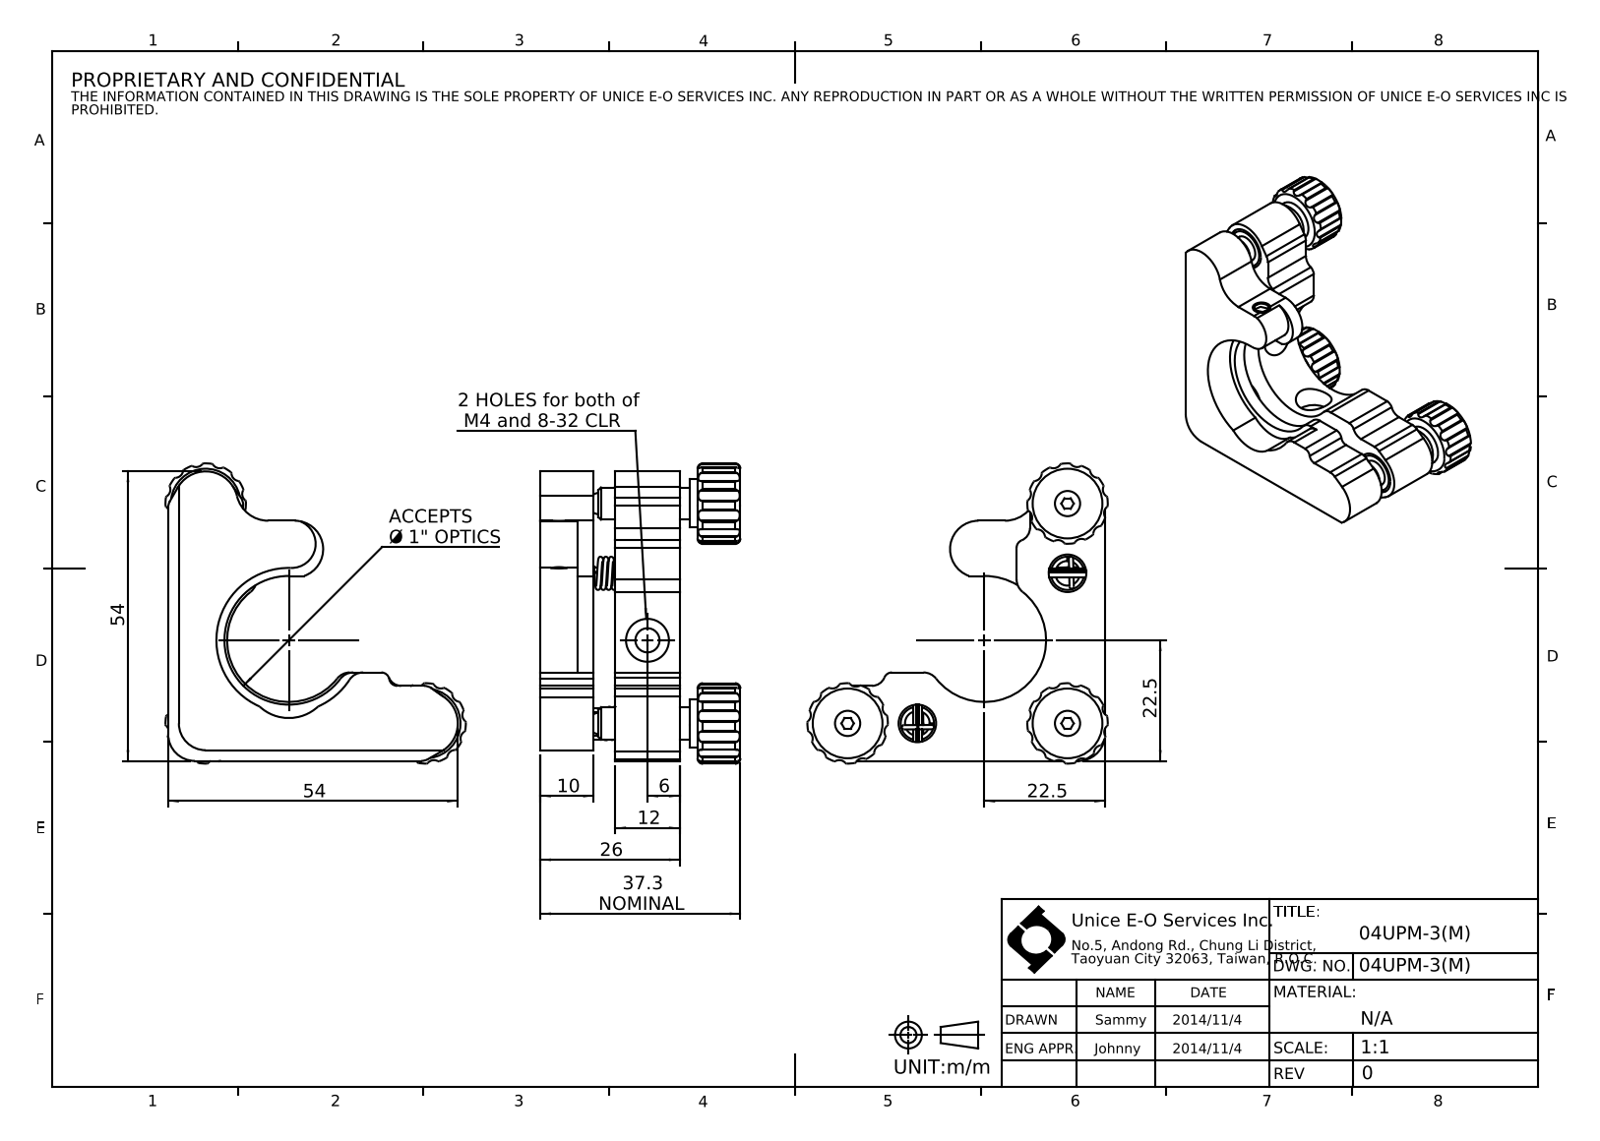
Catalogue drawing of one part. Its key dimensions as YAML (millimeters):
part_name: "04UPM-3(M)"
step_written_by: "SolidWorks 2016 (CONFIG_CONTROL_DESIGN)"
units: millimeters
bodies: {solids: 24, faces: 484, planar: 119, cylindrical: 294, other: 71}
overall_size: [55.95, 55.95, 37.33]
volume: 28064
surface_area: 19263
round_holes:
  - {diameter: 1.2, count: 4}
  - {diameter: 1.7, count: 4}
  - {diameter: 4, count: 3}
  - {diameter: 4.7, count: 3}
  - {diameter: 5.9, count: 3}
  - {diameter: 6, count: 3}
  - {diameter: 9.5, count: 3}
  - {diameter: 4.5, count: 2}
  - {diameter: 7, count: 2}
  - {diameter: 8, count: 2}
  - {diameter: 3.3, count: 1}
  - {diameter: 6.35, count: 1}
round_bosses_or_shafts:
  - {diameter: 1.6, count: 4}
  - {diameter: 9, count: 3}
  - {diameter: 0.6, count: 2}
  - {diameter: 6.3, count: 1}
  - {diameter: 4, count: 1}
  - {diameter: 2.5, count: 1}
partial_cylinders:
  - {radius: 0.3, count: 72}
  - {radius: 1.5, count: 39}
  - {radius: 2.5, count: 6}
  - {radius: 3, count: 4}
  - {radius: 6, count: 3}
  - {radius: 7.5, count: 3}
  - {radius: 5, count: 2}
  - {radius: 4.5, count: 1}
face_to_face_distances: [14, 12, 2, 4, 26, 10, 16, 7, 8, 27.33]
hole_center_spacings: [13, 13.12, 21, 21.1, 28, 41, 49.65, 12.51]
